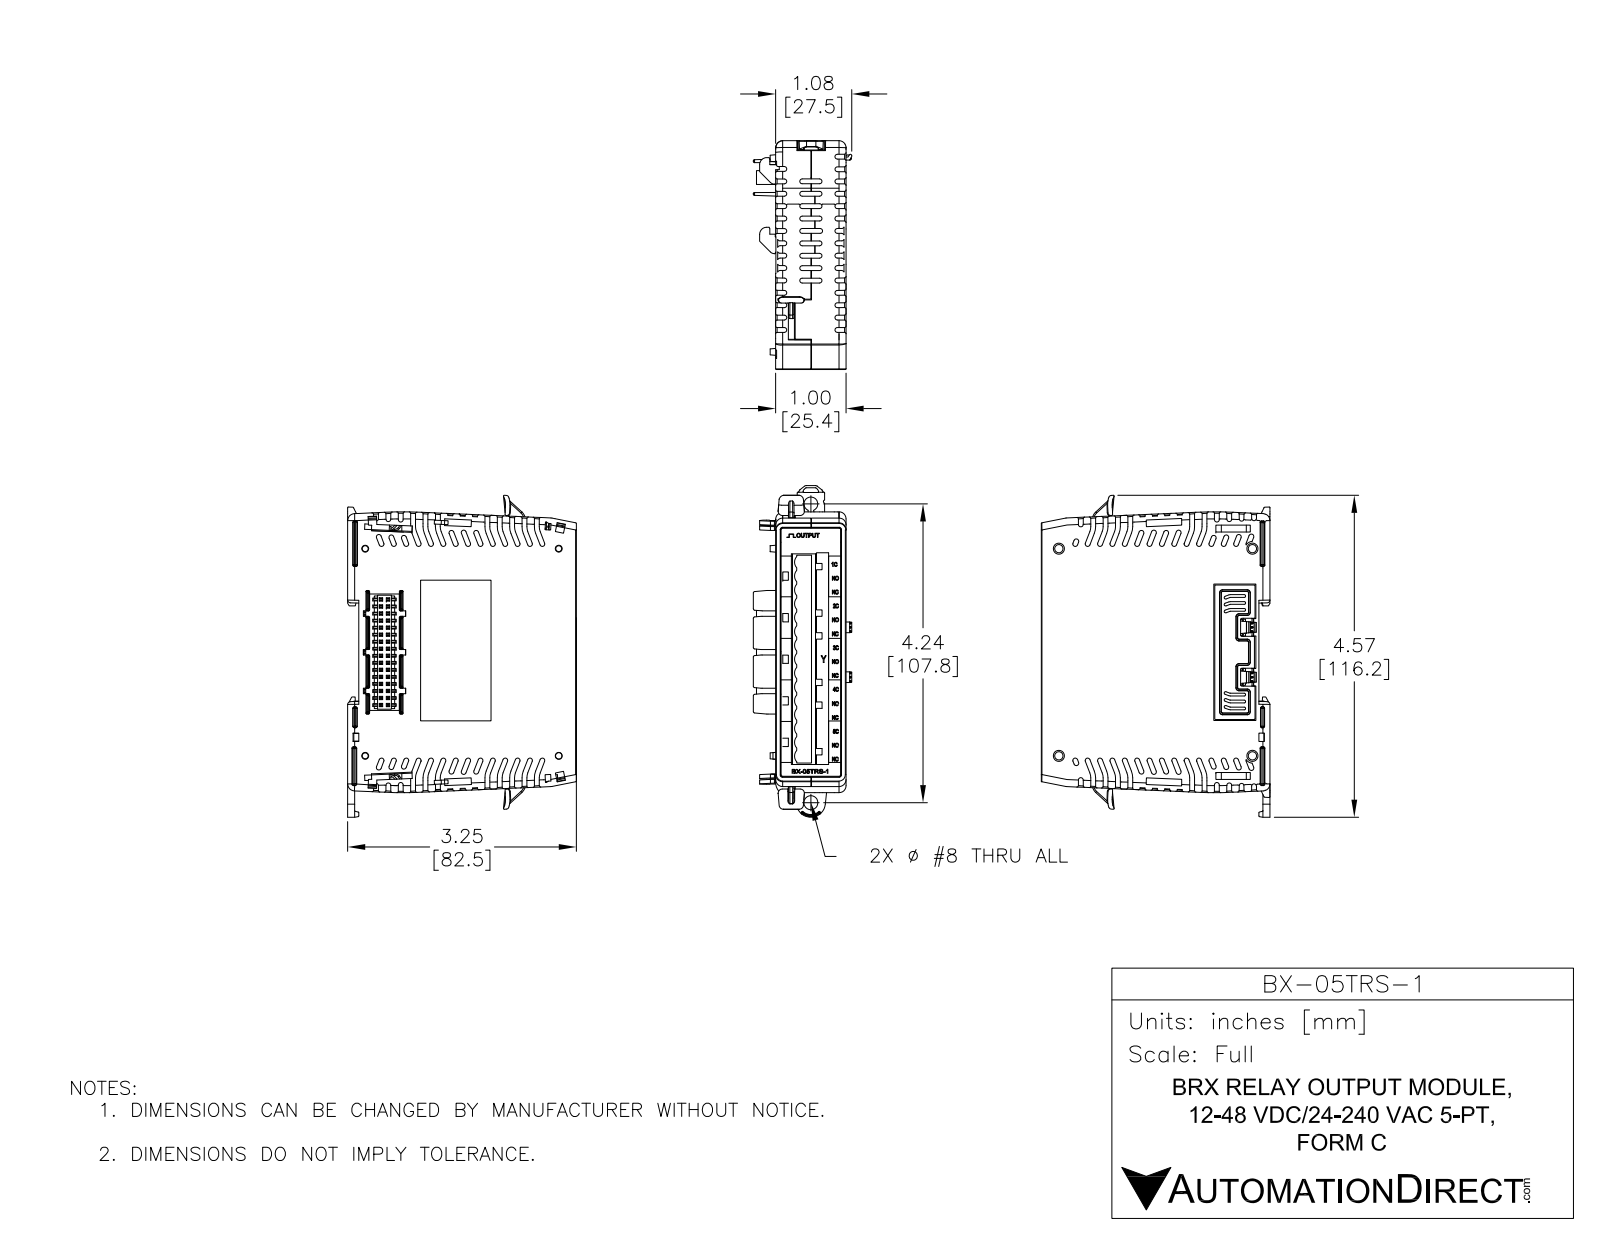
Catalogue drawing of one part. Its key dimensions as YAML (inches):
part_name: "BX-05TRS-1 doo mod 1 comb1 fXT c"
step_written_by: "SolidWorks 2017 (AUTOMOTIVE_DESIGN)"
units: inches
bodies: {solids: 10, faces: 3532, planar: 2641, cylindrical: 387, other: 504}
overall_size: [4.586, 3.311, 1.4]
volume: 11.6
surface_area: 73.37
round_holes:
  - {diameter: 0.047, count: 2}
  - {diameter: 0.065, count: 2}
  - {diameter: 0.118, count: 2}
  - {diameter: 0.118, count: 2}
  - {diameter: 0.199, count: 1}
round_bosses_or_shafts:
  - {diameter: 0.062, count: 2}
  - {diameter: 0.059, count: 2}
partial_cylinders:
  - {radius: 0.01, count: 46}
  - {radius: 0.005, count: 24}
  - {radius: 0.02, count: 22}
  - {radius: 0.008, count: 21}
  - {radius: 0.122, count: 15}
  - {radius: 0.117, count: 14}
  - {radius: 0.039, count: 13}
  - {radius: 0.01, count: 12}
face_to_face_distances: [1, 3.211, 3.22, 0.1, 0.039, 0.475, 3.221, 0.157, 3.053, 3.063]
hole_center_spacings: [0.1, 0.824, 0.919, 1.3, 2.093, 2.193, 2.585, 2.617]
